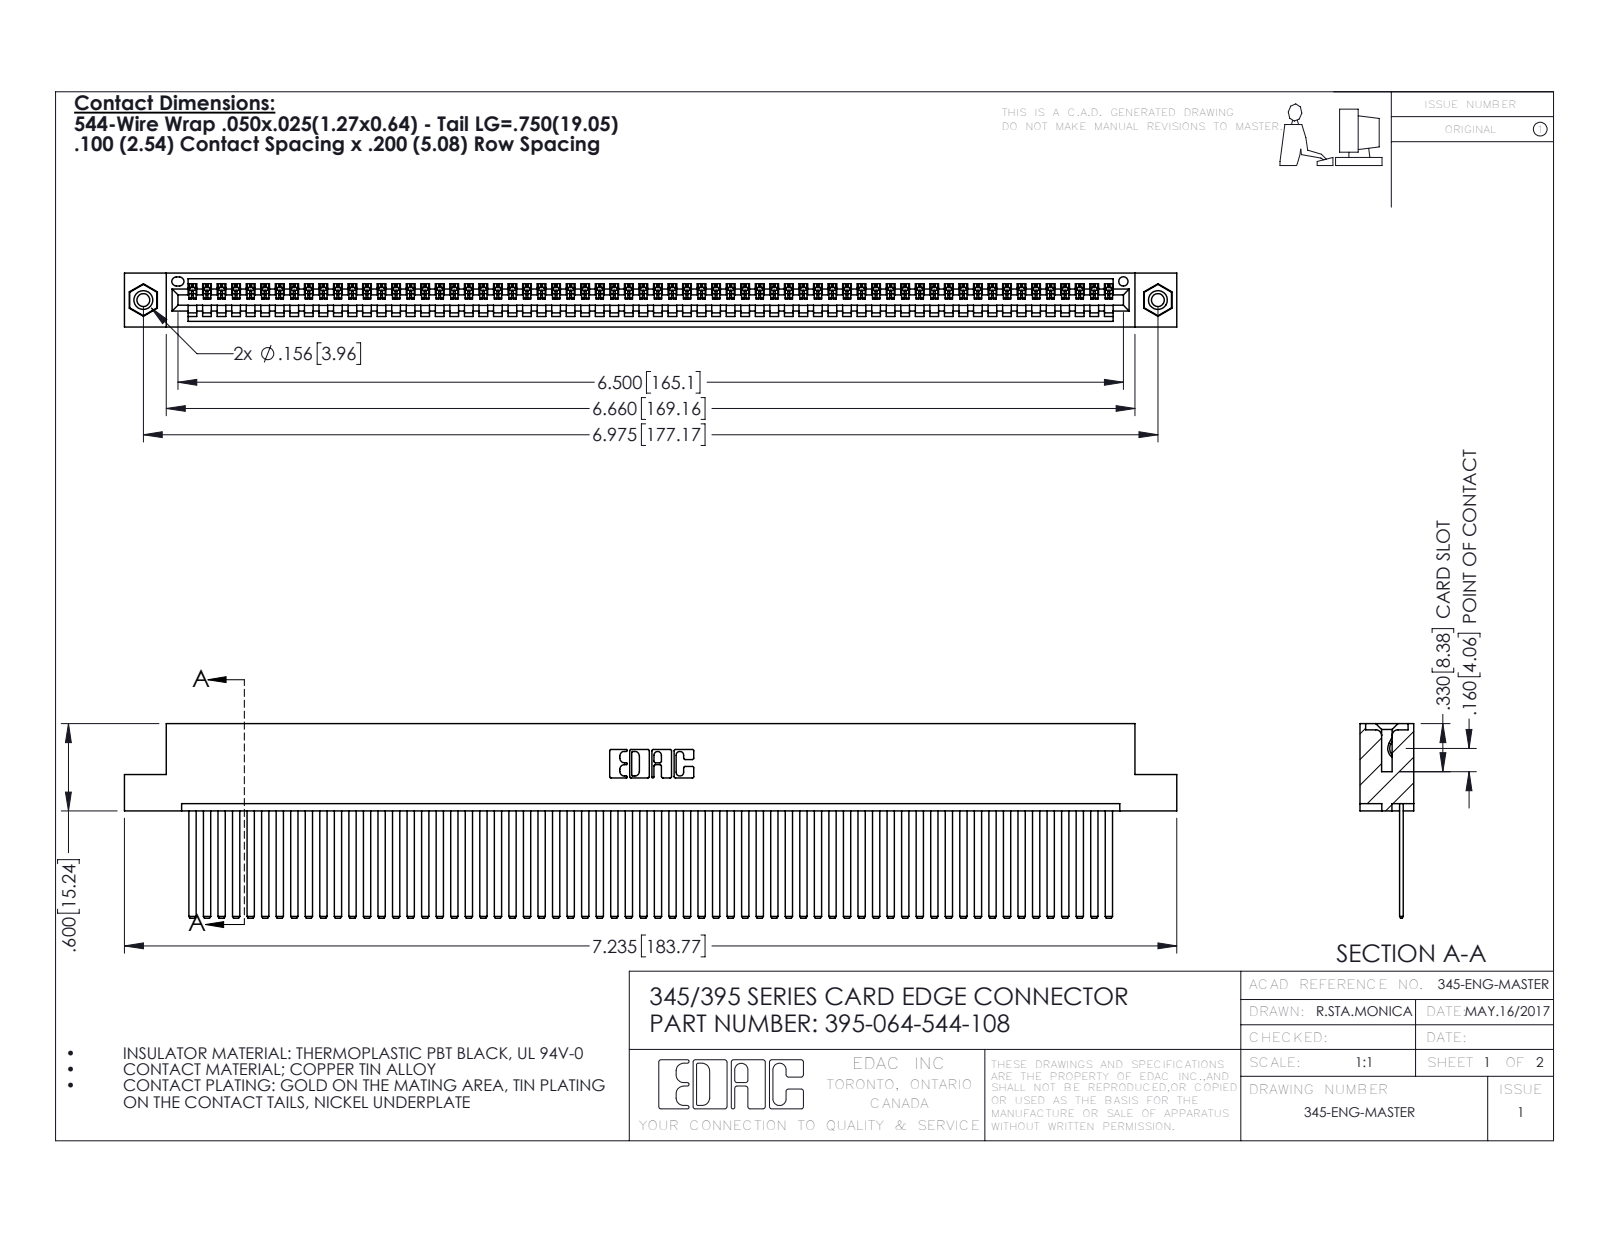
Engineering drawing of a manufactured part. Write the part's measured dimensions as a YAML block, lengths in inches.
part_name: "345-292-001_345-293-144; 345 Part_Flush Mounting Lugs - 0.156 Dia-TI; 395-064-544-108; 345-250-001_345-250-003-102"
step_written_by: "SolidWorks 2016 (CONFIG_CONTROL_DESIGN)"
units: inches
bodies: {solids: 67, faces: 3514, planar: 2416, cylindrical: 1082, other: 16}
overall_size: [7.235, 1.337, 0.37]
volume: 1.121
surface_area: 41.78
round_holes:
  - {diameter: 0.089, count: 2}
  - {diameter: 0.125, count: 2}
  - {diameter: 0.156, count: 2}
  - {diameter: 0.064, count: 1}
round_bosses_or_shafts:
  - {diameter: 0.155, count: 2}
partial_cylinders:
  - {radius: 0.006, count: 128}
  - {radius: 0.01, count: 22}
  - {radius: 0.007, count: 6}
  - {radius: 0.031, count: 6}
  - {radius: 0.026, count: 3}
  - {radius: 0.031, count: 2}
  - {radius: 0.04, count: 2}
  - {radius: 0.014, count: 1}
face_to_face_distances: [0.072, 0.298, 0.025, 0.098, 0.272, 0.37, 0.2, 0.225, 0.149, 0.072]
hole_center_spacings: [0.27, 6.739, 6.975]
